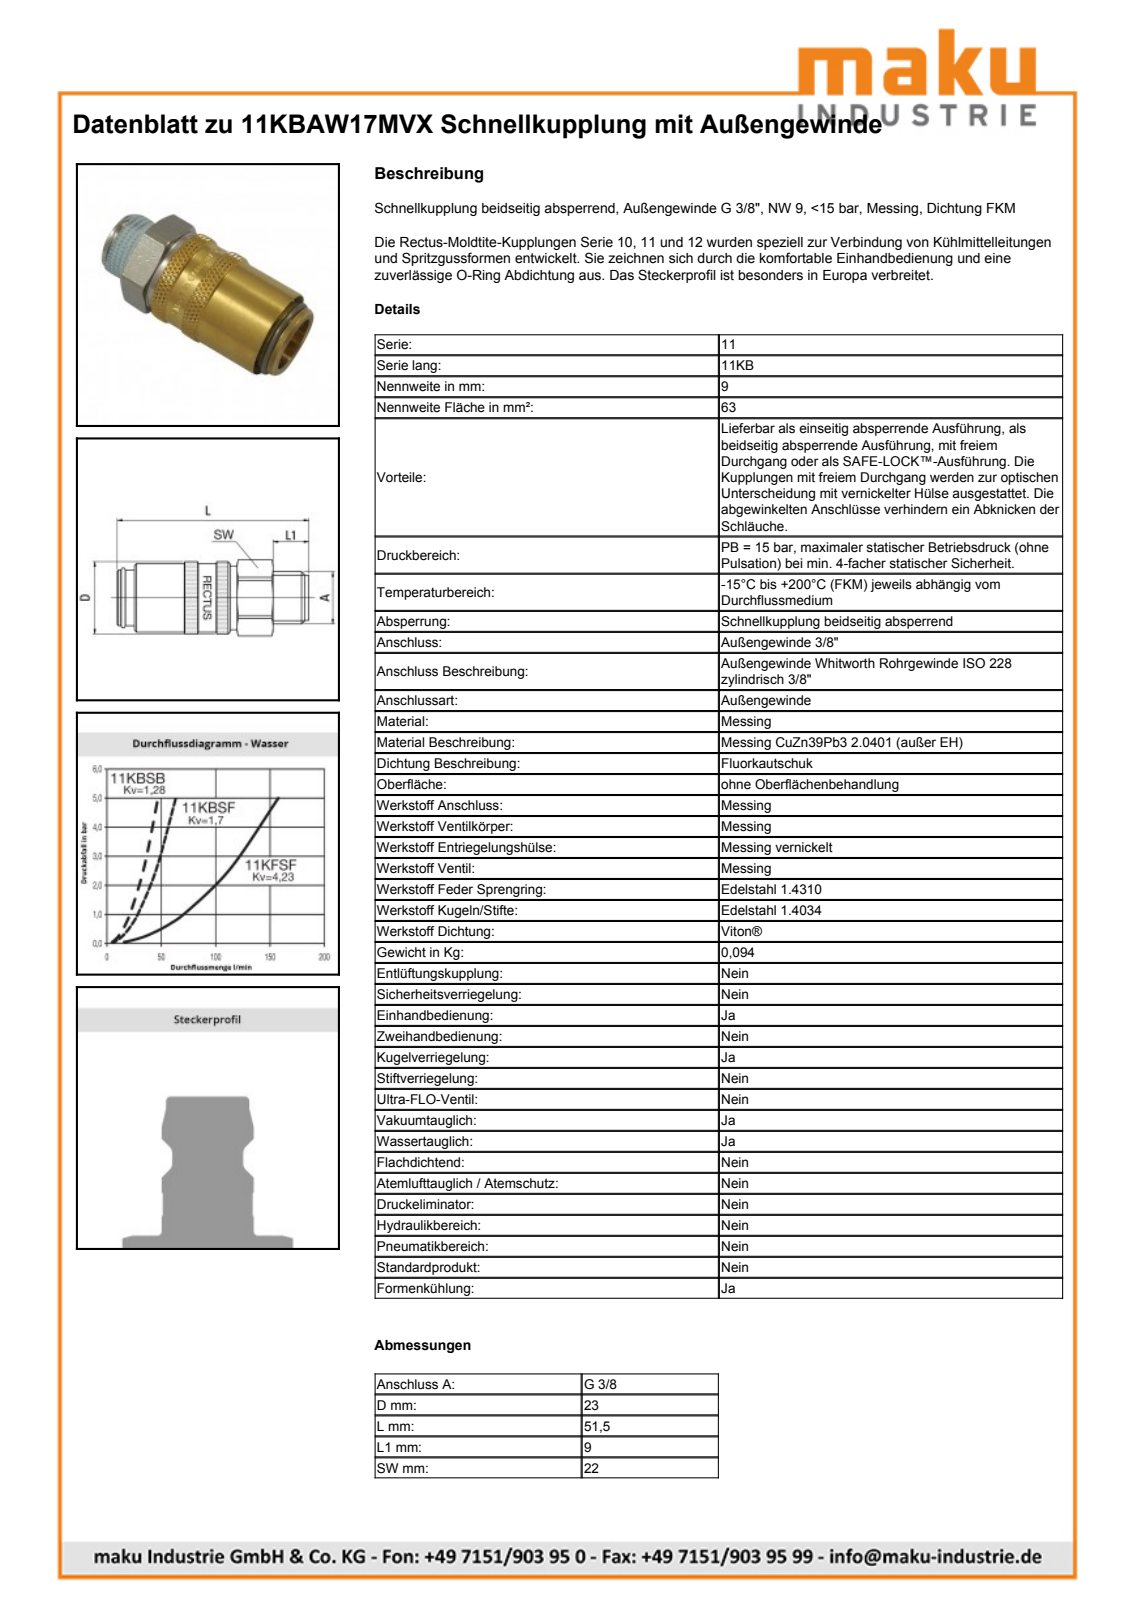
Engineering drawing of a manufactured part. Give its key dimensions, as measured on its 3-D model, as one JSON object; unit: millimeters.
{"part_name": "D113337", "step_written_by": "Autodesk Inventor 2013 (AUTOMOTIVE_DESIGN)", "units": "millimeters", "bodies": {"solids": 2, "faces": 680, "planar": 246, "cylindrical": 72, "other": 362}, "overall_size": [51.6, 24.64, 23.52], "volume_mm3": 18003, "surface_area_mm2": 5345, "round_holes": [[20.8, 1]], "round_bosses_or_shafts": [[23.2, 1], [22.1, 1], [21.64, 1], [20.5, 1], [18, 1], [16.66, 1], [16.45, 1], [14.7, 1]], "partial_cylinders_radius": [[9, 1], [10.95, 1], [12.4, 1]], "face_to_face_distances": [9, 22, 42.6, 51.6, 5.2, 37.4, 46.4, 17.45, 1.55, 4]}
